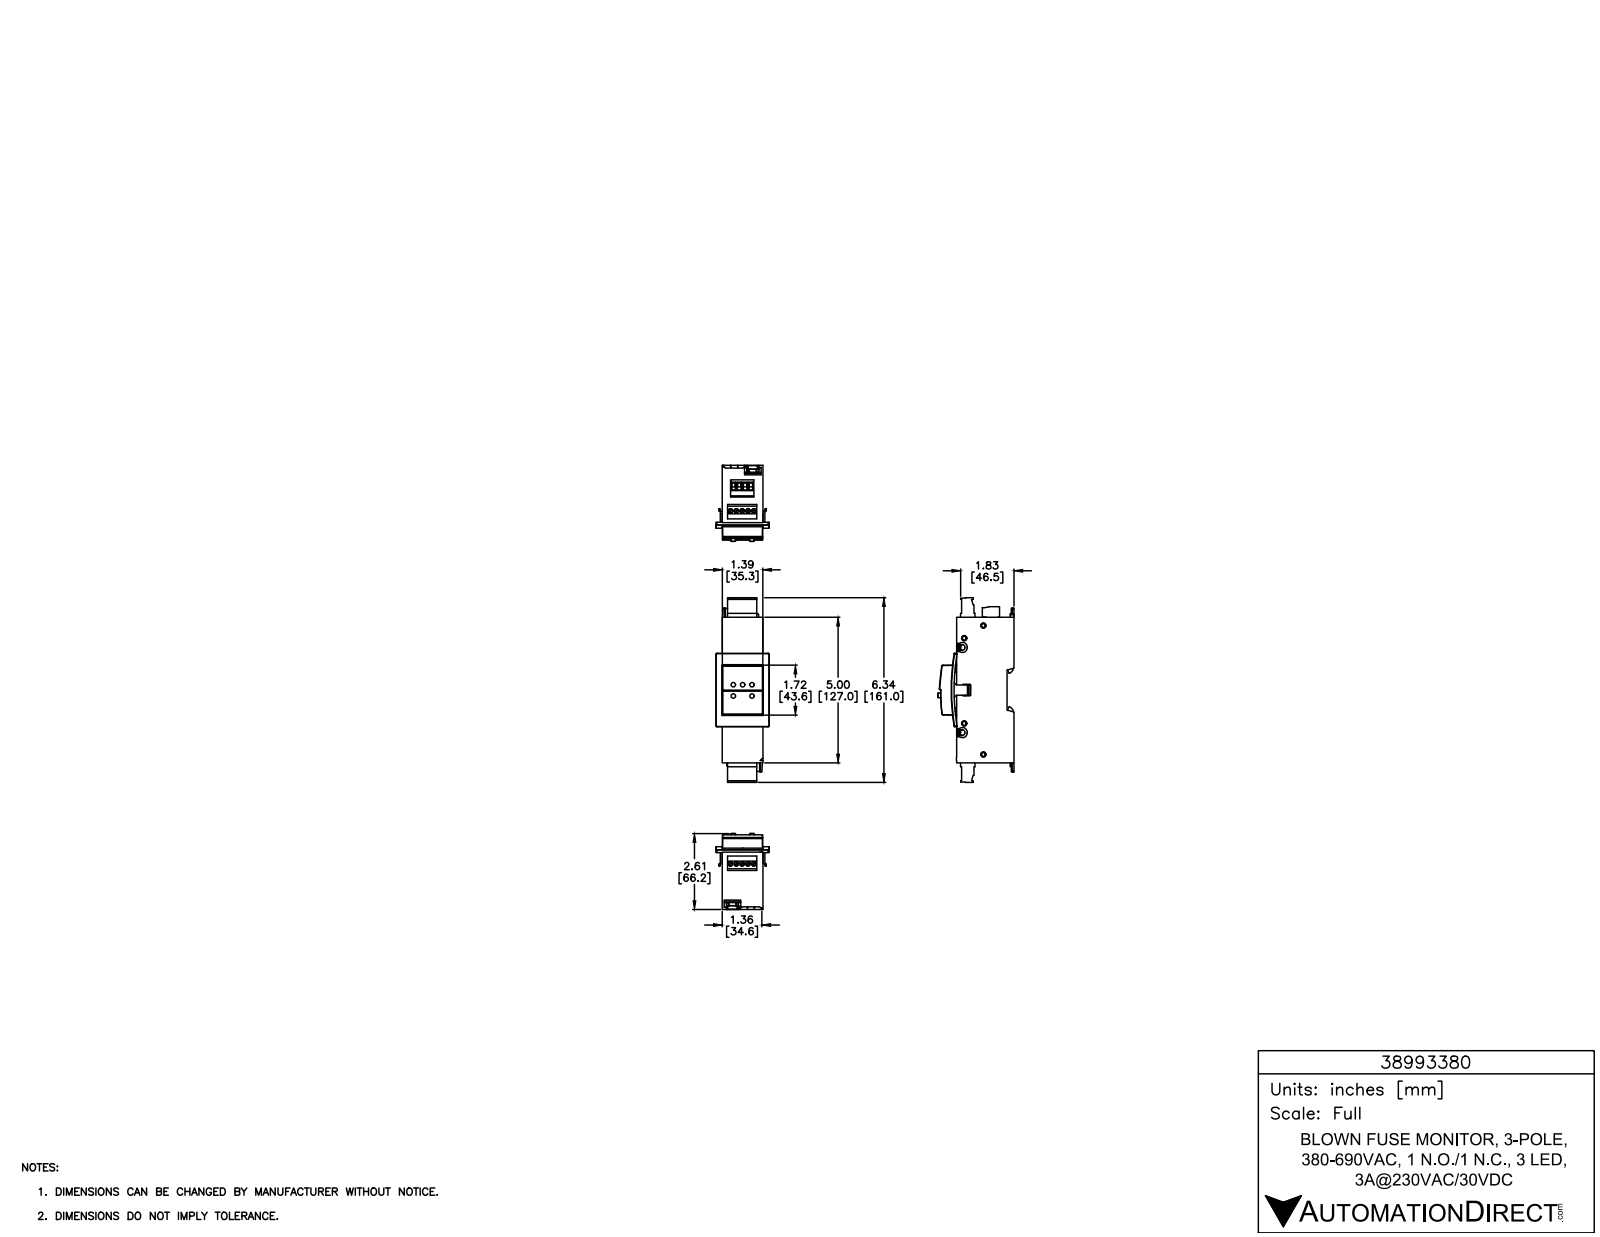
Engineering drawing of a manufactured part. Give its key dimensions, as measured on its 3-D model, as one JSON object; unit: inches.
{"part_name": "38993380", "step_written_by": "SolidWorks 2015 (AUTOMOTIVE_DESIGN)", "units": "inches", "bodies": {"solids": 1, "faces": 847, "planar": 521, "cylindrical": 248, "other": 78}, "overall_size": [6.339, 2.614, 1.831], "volume_in3": 14.85, "surface_area_in2": 69.01, "round_holes": [[0.157, 9], [0.181, 4], [0.165, 2]], "round_bosses_or_shafts": [[0.149, 9], [0.165, 4]], "partial_cylinders_radius": [[0.008, 24], [0.009, 24], [0.023, 24], [0.039, 15], [0.01, 12], [0.02, 10], [0.047, 4], [0.059, 4]], "face_to_face_distances": [1.398, 1.732, 1.969, 0.236, 5, 0.699, 0.402, 0.213, 0.17, 1.562], "hole_center_spacings": [0.2, 0.4, 0.6, 0.386, 0.791, 0.8, 1.255, 2.467]}
